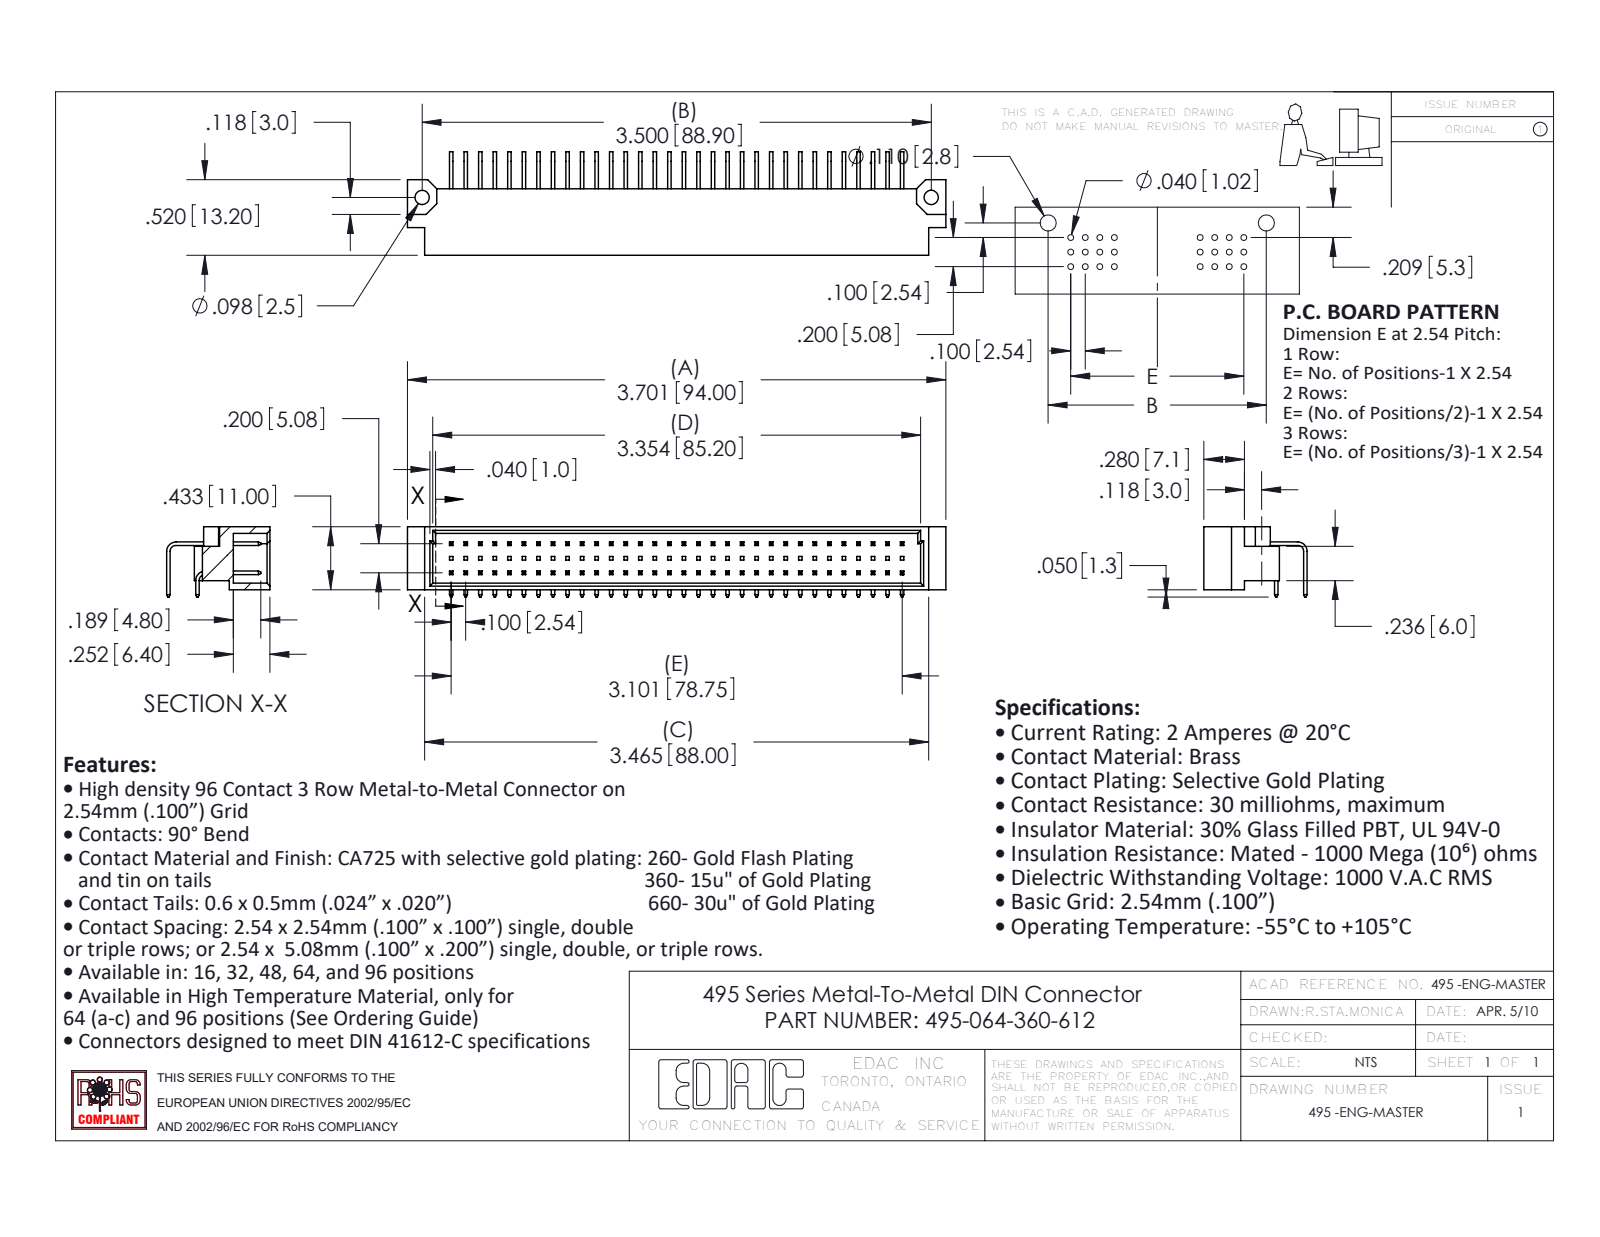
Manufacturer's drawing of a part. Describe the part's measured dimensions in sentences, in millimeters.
The part is named "495-290-3; 495-064-360-612; 495 Part_96; 495-290-1". Its 3-D file was written by "SolidWorks 2020 (AUTOMOTIVE_DESIGN)". It is 65 solids with 1585 faces: 1453 planar, 132 cylindrical and 0 other. Overall it measures 94 by 18.05 by 12.27 millimeters. Its volume is 6 391 cubic millimeters and its surface area 9 910 square millimeters. Round holes: 2 of diameter 2.49. Partial cylindrical surfaces (rounded edges, fillets, slot ends): 2 of radius 1.02, 2 of radius 1.65. The main face-to-face distances are 1.14, 9.86, 0.61, 5.08, 5.2, 11, 2.54, 8.72, 1.6, 9.4. The hole center spacings are 88.9.
